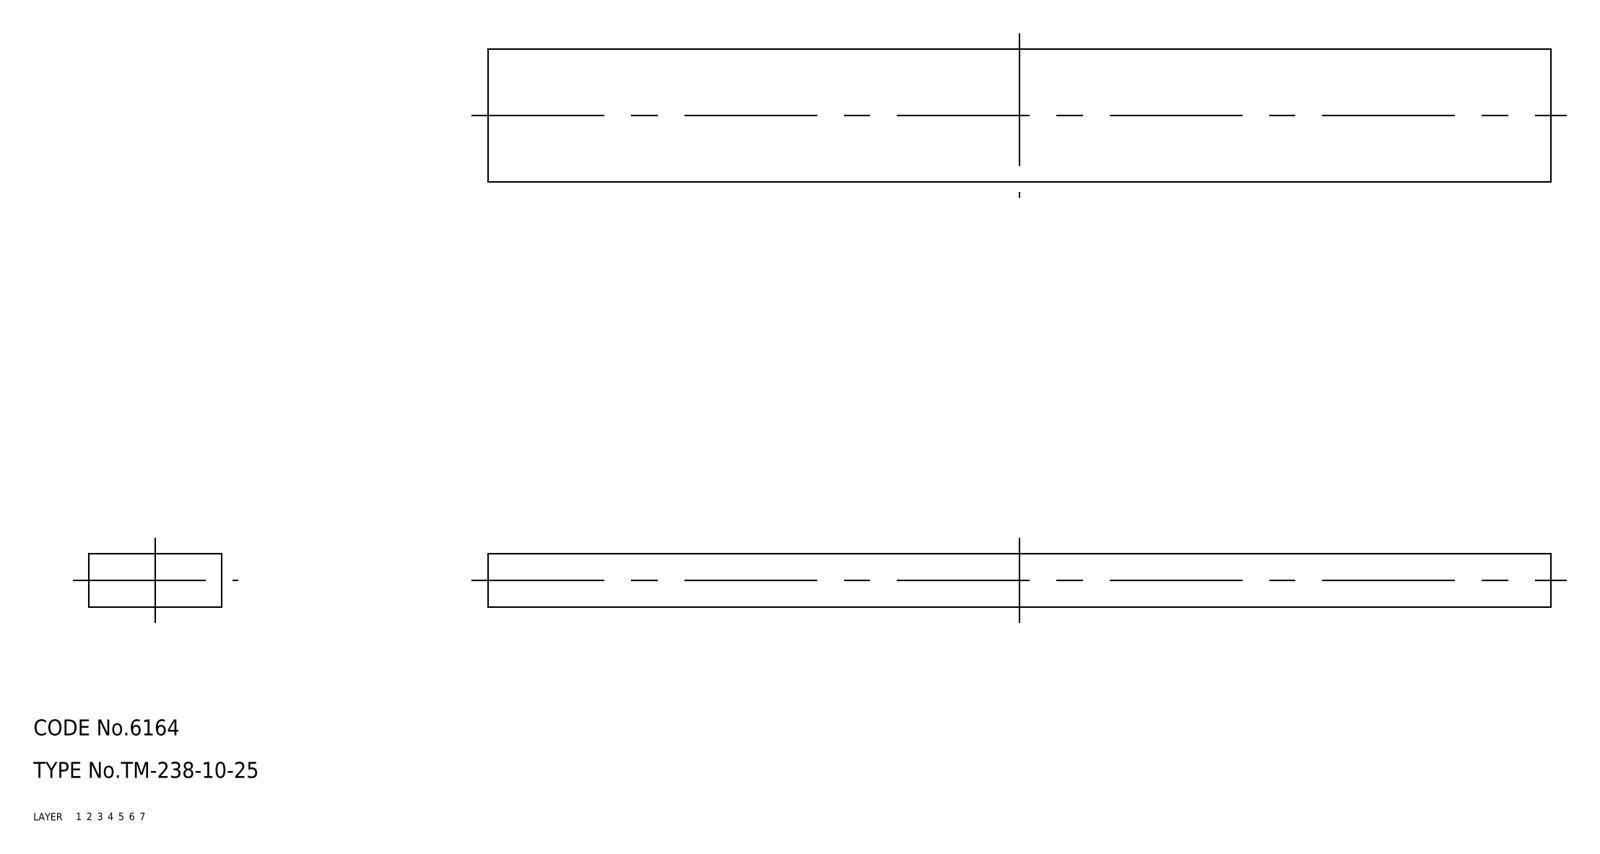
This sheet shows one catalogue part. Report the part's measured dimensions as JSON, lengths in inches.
{"part_name": "rubber foam", "step_written_by": "CADfix (AUTOMOTIVE_DESIGN)", "units": "inches", "bodies": {"solids": 1, "faces": 6, "planar": 0, "cylindrical": 0, "other": 6}, "overall_size": [7.874, 0.984, 0.394], "volume_in3": 3.051, "surface_area_in2": 22.48}
